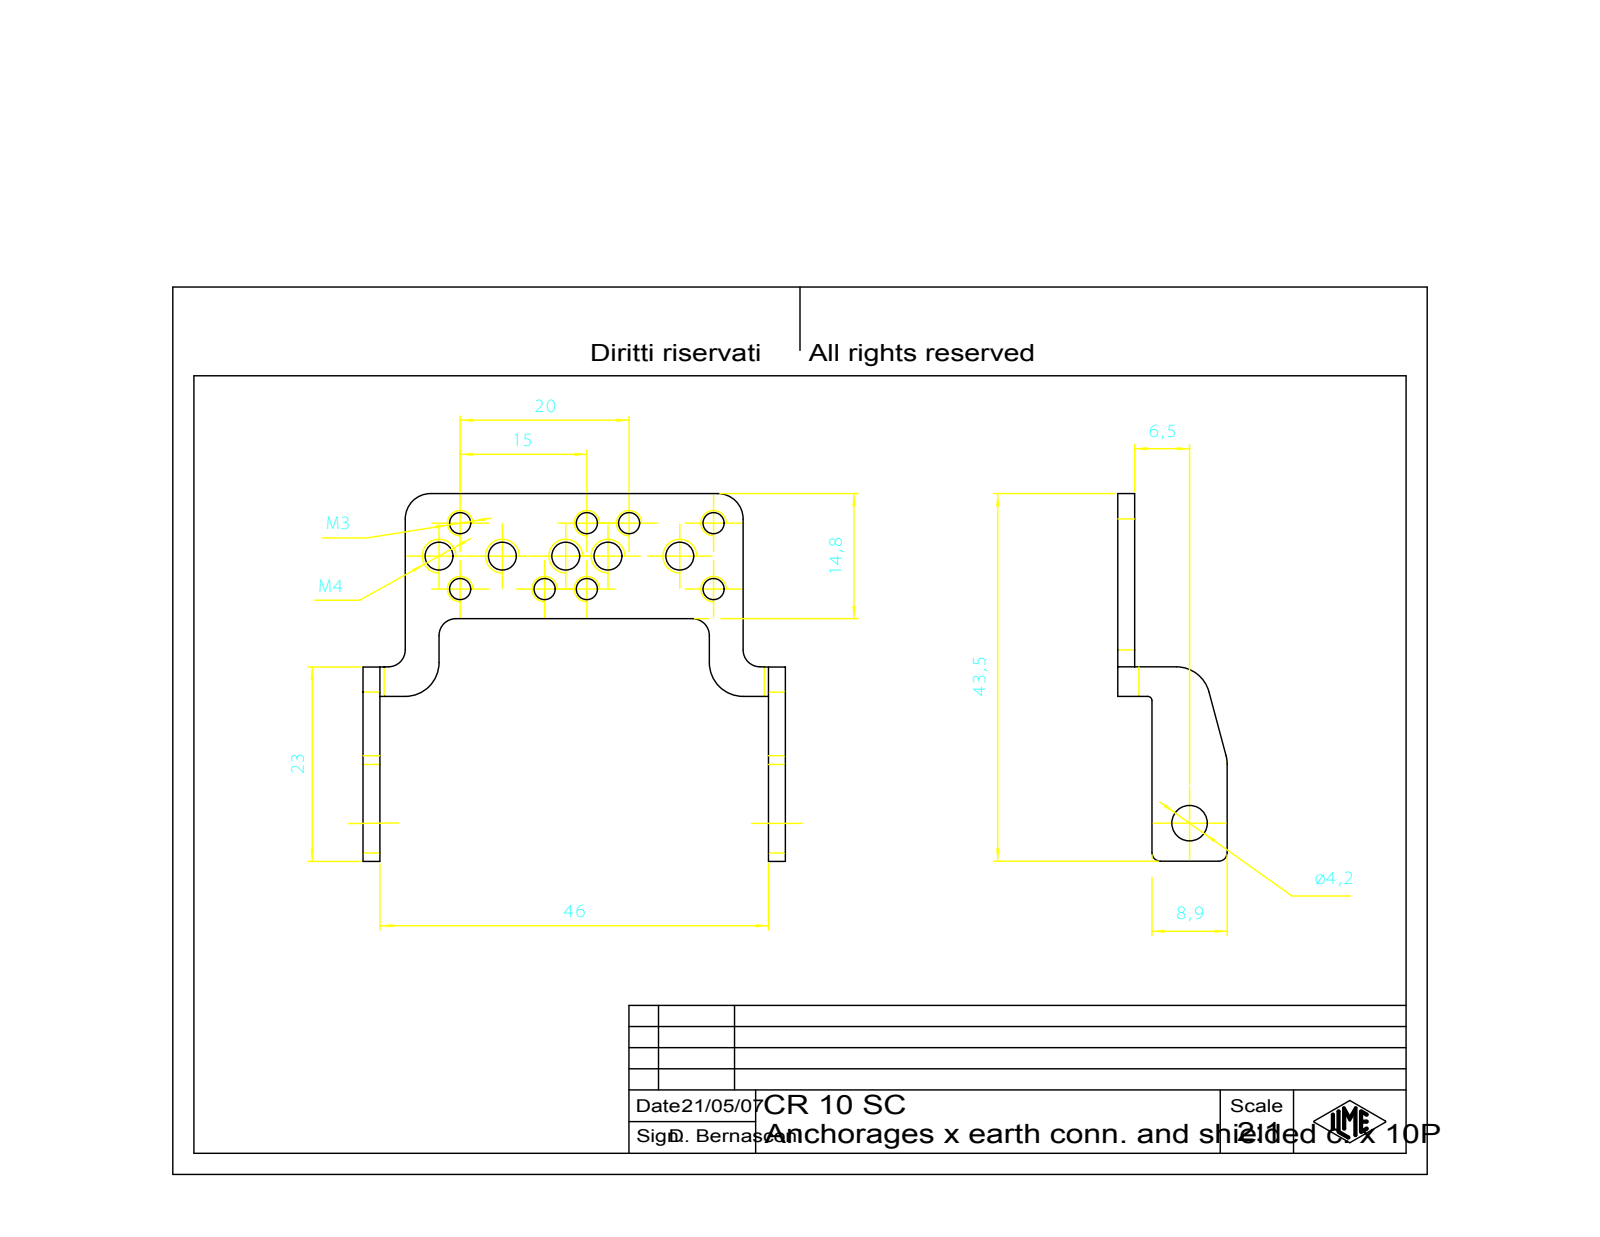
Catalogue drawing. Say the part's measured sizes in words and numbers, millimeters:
The part is named "CR_10_SC". Its 3-D file was written by "OneSpace Modeling 15.50B 03-Nov-2007 (C) CoCreate Software GmbH (AUTOMOTIVE_DESIGN)". It is 1 solid with 76 faces: 24 planar, 52 cylindrical and 0 other. Overall it measures 50 by 43.5 by 12.95 millimeters. Its volume is 1 932 cubic millimeters and its surface area 2 748 square millimeters. Round holes: 8 of diameter 2.5, 5 of diameter 3.3, 1 of diameter 4.2. Partial cylindrical surfaces (rounded edges, fillets, slot ends): 4 of radius 2, 4 of radius 4, 3 of radius 0.5, 2 of radius 1, 2 of radius 2.5, 2 of radius 3. The main face-to-face distances are 2, 48, 50, 46, 4.05, 2.05, 5, 45, 3, 43. The hole center spacings are 4.63, 17.93, 13.09, 15, 16.91, 5, 6.34, 7.8.
